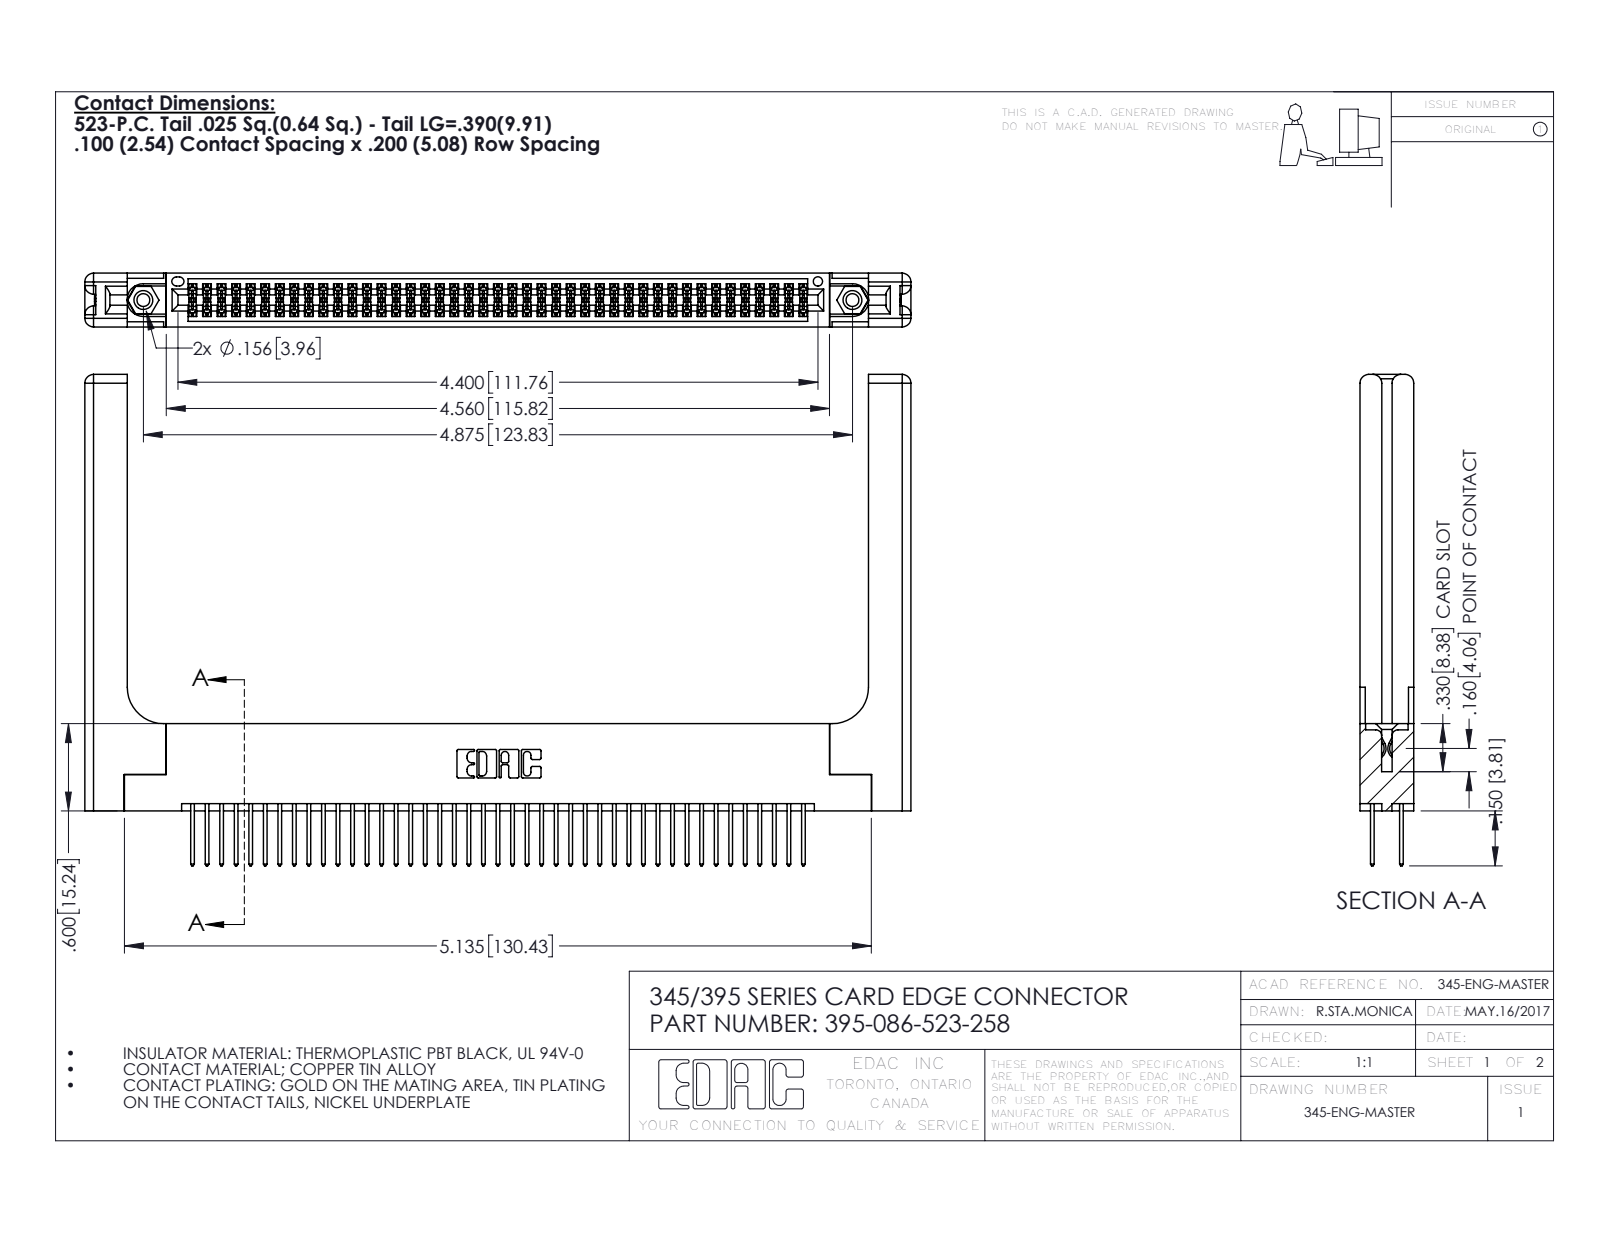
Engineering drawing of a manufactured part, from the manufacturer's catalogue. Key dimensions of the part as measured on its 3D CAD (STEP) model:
Part name (STEP PRODUCT): 395-086-523-258; 345-292-001_345-293-123; 345-220-058_345-220-058; 345-250-001_345-250-001-102 (+1 more)
STEP written by: SolidWorks 2016 (CONFIG_CONTROL_DESIGN)
Units: inches
Bodies: 91 solids, 4682 faces (3066 planar, 1556 cylindrical, 60 other)
Overall size (bounding box): 5.679 × 3.377 × 0.37
Volume: 1.384 in³ · Surface area: 41.63 in²
Round holes (diameter × count): ⌀0.089 ×2, ⌀0.125 ×2, ⌀0.156 ×2, ⌀0.064 ×1
Round bosses / shafts (diameter × count): ⌀0.155 ×2
Partial cylindrical surfaces — rounded edges, fillets, slot ends (radius × count): R0.006 ×129, R0.01 ×86, R0.01 ×22, R0.06 ×16, R0.007 ×6, R0.031 ×6, R0.026 ×3, R0.014 ×2
Main face-to-face distances: 0.072, 0.298, 0.37, 0.2, 0.098, 0.272, 0.025, 0.225, 0.175, 0.148
Hole centre spacings: 0.27, 4.639, 4.875
